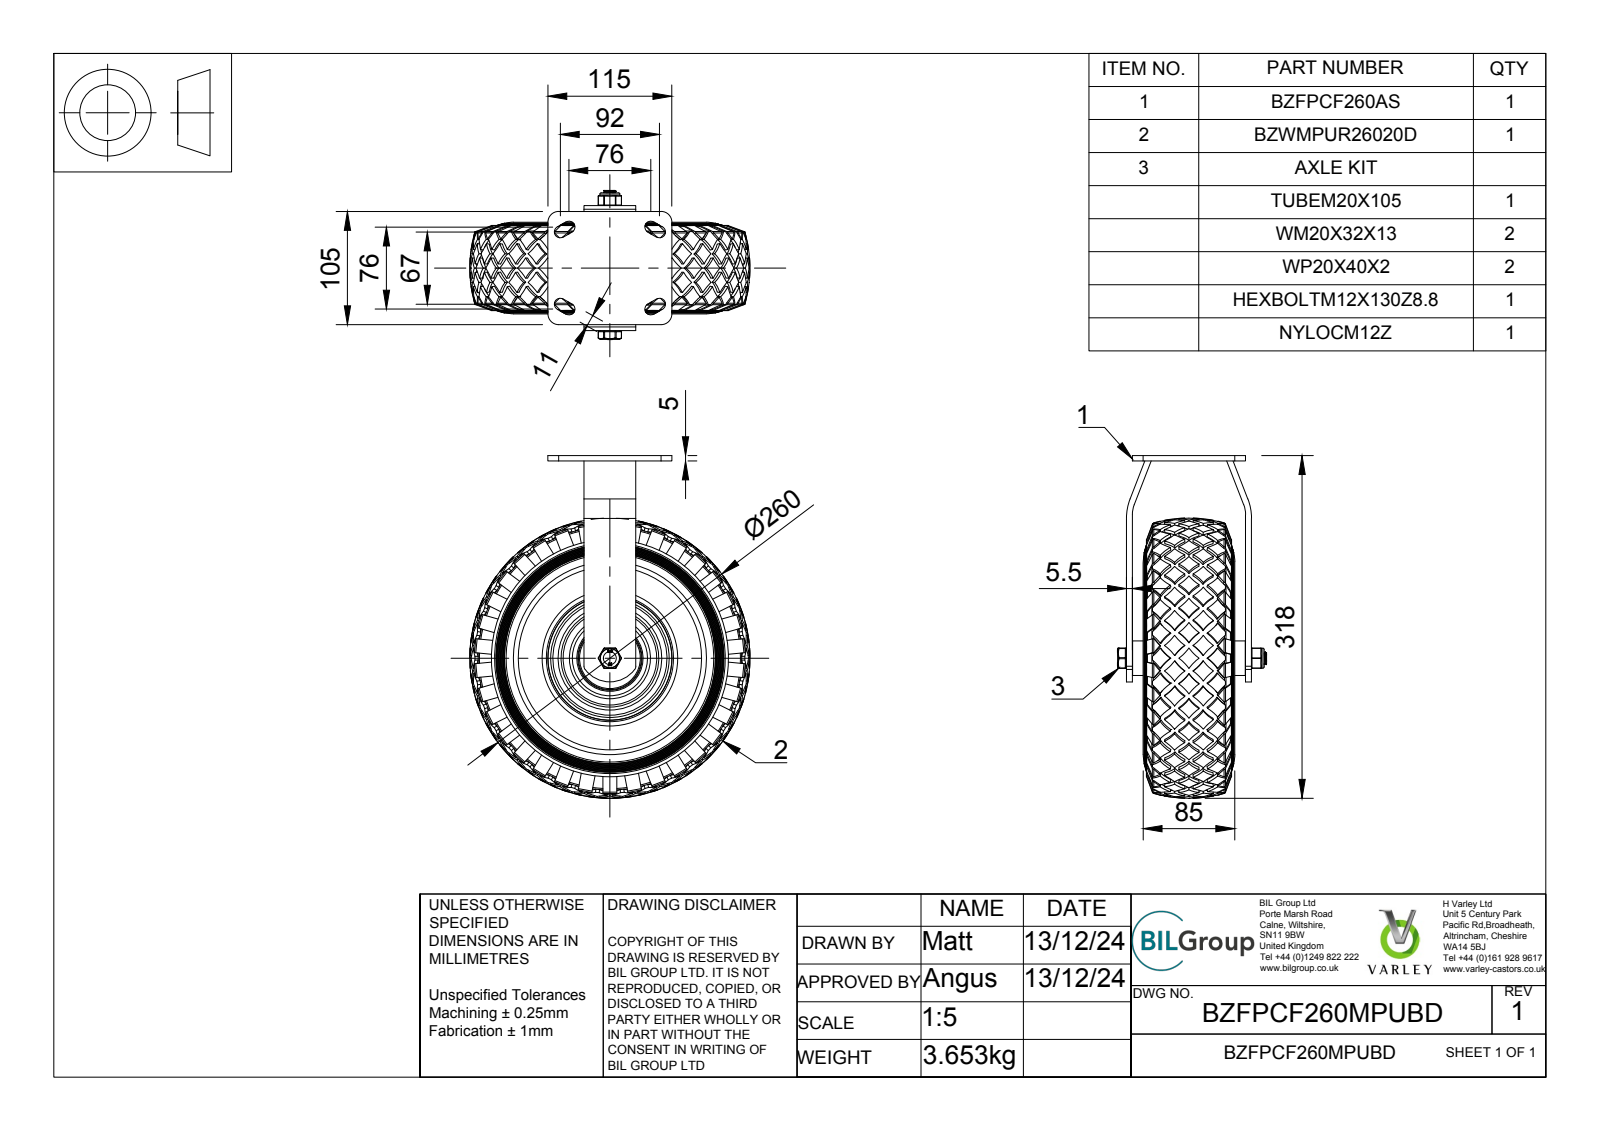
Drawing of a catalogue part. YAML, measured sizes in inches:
part_name: "BZFPCF260MPUBD v4; BZFPCF260AS v1; BZFPCF260AS; FABRICATED STEEL BRACKET (+8 more)"
step_written_by: "Autodesk Translation Framework v13.20.0.188 (AP242_MANAGED_MODEL_BASED_3D_ENGINEERING_MIM_LF)"
units: inches
bodies: {solids: 23, faces: 2160, planar: 603, cylindrical: 321, other: 1236}
overall_size: [12.519, 10.235, 5.445]
volume: 224.6
surface_area: 626.9
round_holes:
  - {diameter: 0.031, count: 2}
  - {diameter: 0.354, count: 1}
  - {diameter: 0.472, count: 1}
  - {diameter: 0.492, count: 1}
  - {diameter: 0.512, count: 1}
  - {diameter: 0.551, count: 1}
  - {diameter: 0.787, count: 1}
  - {diameter: 0.827, count: 1}
  - {diameter: 1.378, count: 1}
  - {diameter: 3.661, count: 1}
  - {diameter: 3.937, count: 1}
  - {diameter: 4.37, count: 1}
round_bosses_or_shafts:
  - {diameter: 0.295, count: 8}
  - {diameter: 8.661, count: 1}
  - {diameter: 2.421, count: 1}
  - {diameter: 2.283, count: 1}
  - {diameter: 1.476, count: 1}
  - {diameter: 1.339, count: 1}
  - {diameter: 1.28, count: 1}
  - {diameter: 1.26, count: 1}
partial_cylinders:
  - {radius: 0.079, count: 68}
  - {radius: 4.758, count: 34}
  - {radius: 0.02, count: 24}
  - {radius: 0.217, count: 8}
  - {radius: 0.039, count: 6}
  - {radius: 0.016, count: 4}
  - {radius: 0.03, count: 4}
  - {radius: 0.394, count: 4}
face_to_face_distances: [0.217, 4.35, 0.197, 0.591, 0.512, 4.134, 0.394, 4.567, 0.118, 3.15]
hole_center_spacings: [0.297, 0.117, 1.349, 1.388, 1.645]
